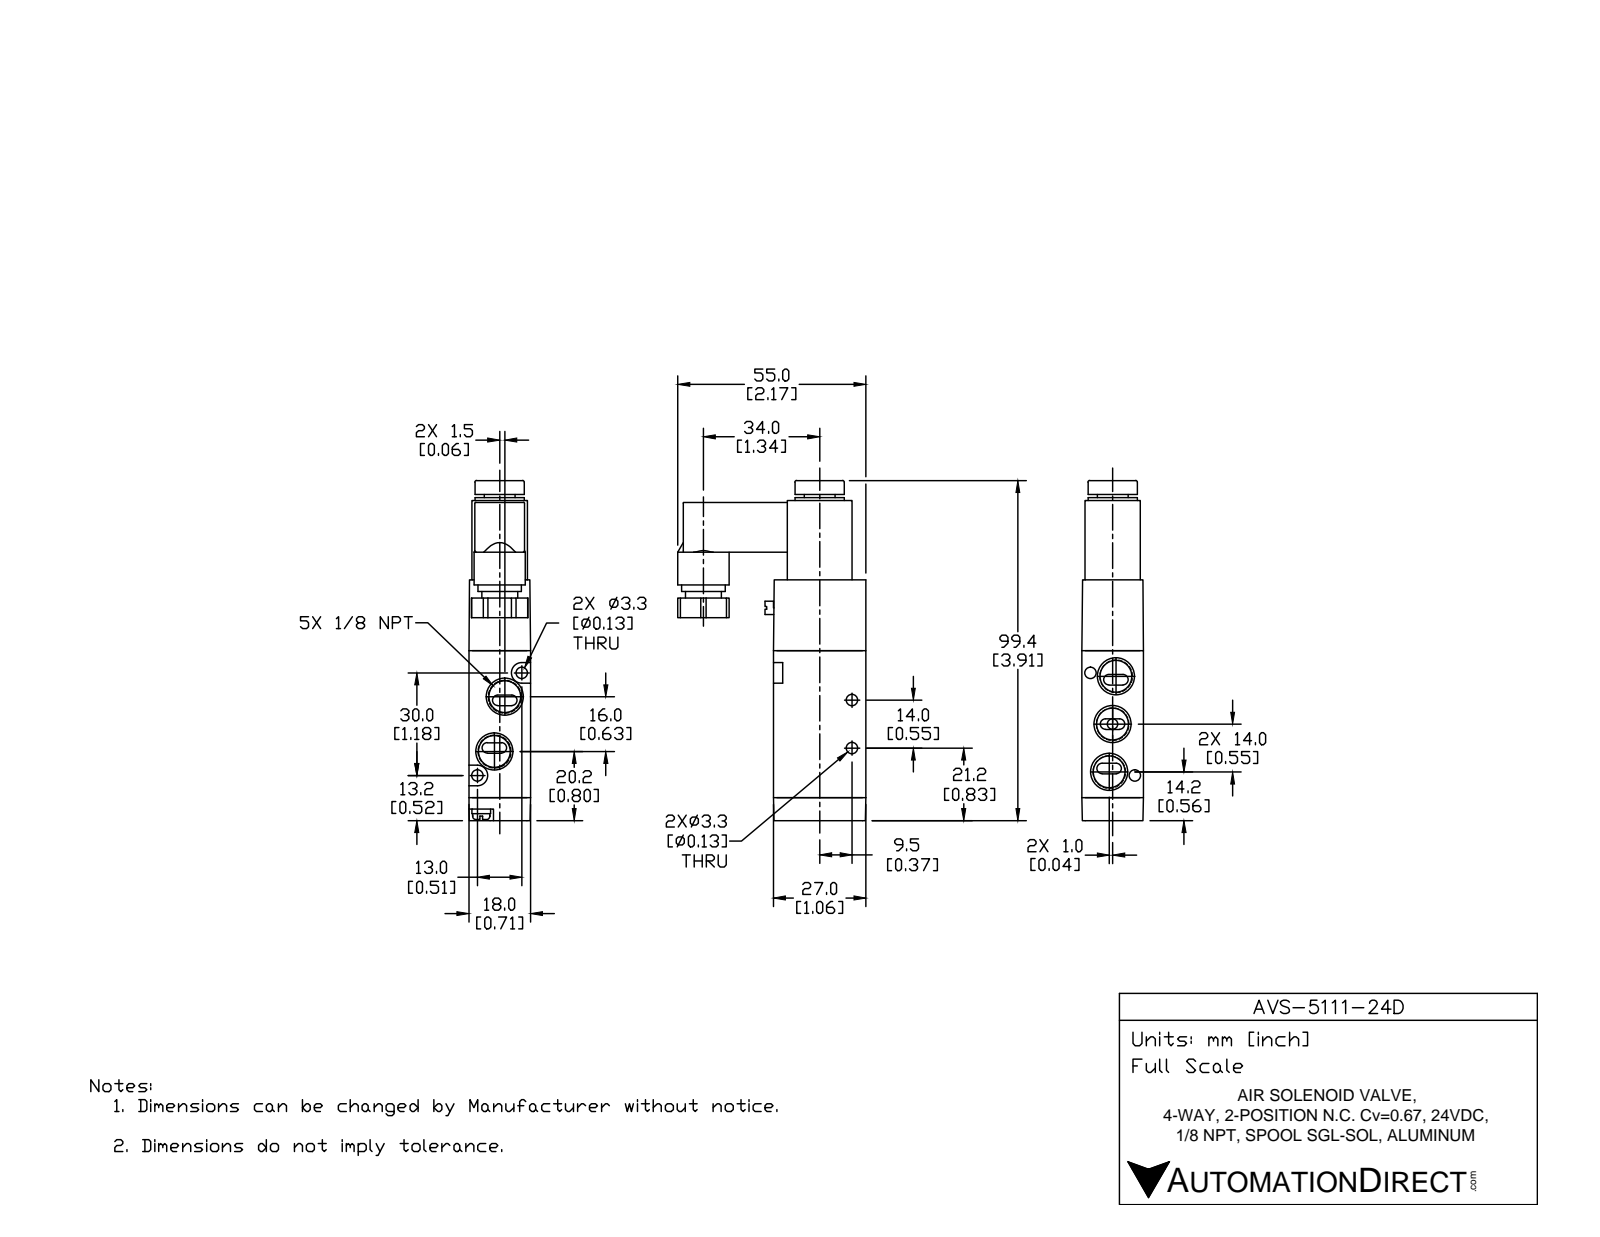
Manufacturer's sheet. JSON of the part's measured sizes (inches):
{"part_name": "AVS-5111-24D", "step_written_by": "SolidWorks 2015 (CONFIG_CONTROL_DESIGN)", "units": "inches", "bodies": {"solids": 4, "faces": 183, "planar": 90, "cylindrical": 67, "other": 26}, "overall_size": [3.917, 2.165, 0.709], "volume_in3": 2.832, "surface_area_in2": 25.98, "round_holes": [[0.332, 5], [0.13, 3], [0.126, 1], [0.366, 1]], "round_bosses_or_shafts": [[0.591, 1], [0.567, 1], [0.504, 1], [0.413, 1], [0.354, 1], [0.268, 1]], "partial_cylinders_radius": [[0.061, 10], [0.02, 8], [0.012, 4], [0.039, 4], [0.118, 2]], "face_to_face_distances": [0.709, 1.693, 0.069, 0.64, 0.032, 0.571, 1.063, 0.152, 0.264, 1.957], "hole_center_spacings": [0.298, 0.553, 0.644, 1.162, 0.246, 0.269, 0.317, 0.322]}
